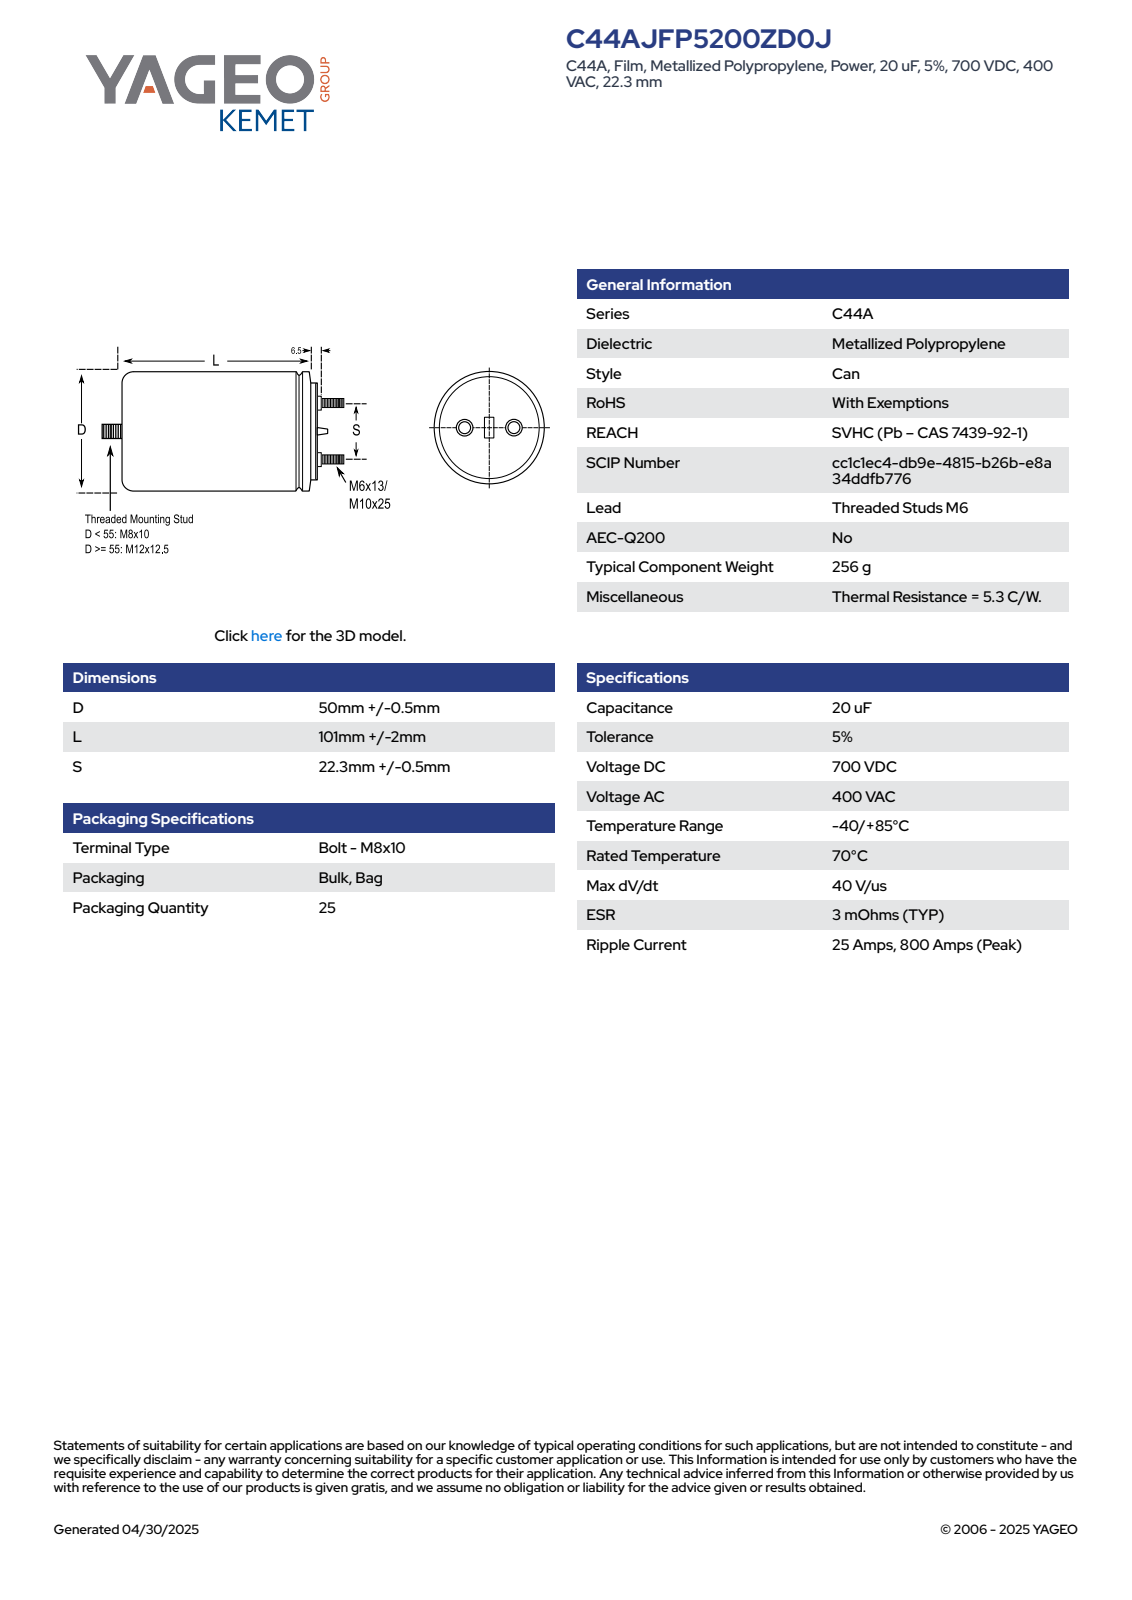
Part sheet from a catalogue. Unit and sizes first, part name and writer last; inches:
Units: inches
Overall size (bounding box): 5.217 × 1.988 × 1.988
Round bosses / shafts (diameter × count): ⌀0.354 ×2, ⌀0.236 ×2, ⌀1.988 ×1, ⌀1.559 ×1, ⌀0.315 ×1
Partial cylindrical surfaces — rounded edges, fillets, slot ends (radius × count): R0.994 ×1
Main face-to-face distances: 4.252, 4.311, 0.059, 4.823, 0.571, 0.512, 0.394, 4.646, 4.705, 5.217
Volume: 12.95 in³ · Surface area: 33.42 in²
Bodies: 1 solid, 102 faces (29 planar, 34 cylindrical, 39 other)
Part name (STEP PRODUCT): CFP_C44A_50X101_D50.5L103S22.3
STEP written by: SolidWorks 2014 (AUTOMOTIVE_DESIGN)
